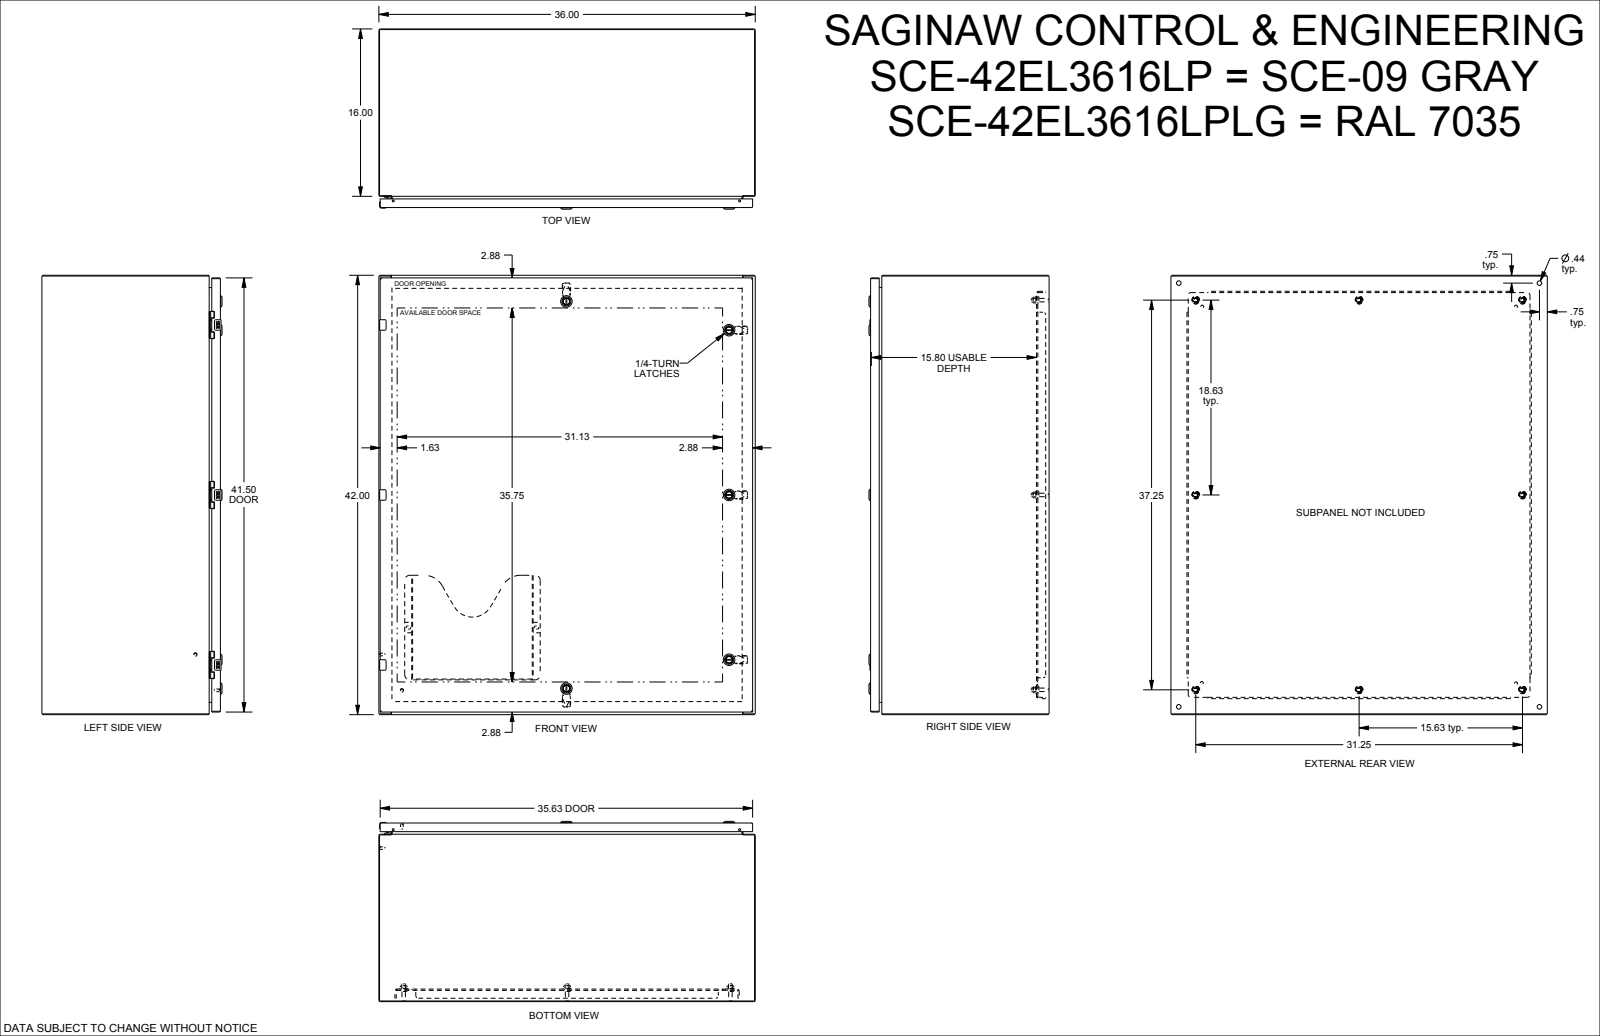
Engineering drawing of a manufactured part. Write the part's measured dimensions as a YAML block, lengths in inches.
part_name: "SCE-42EL3616LPLG"
step_written_by: "SolidWorks 2019 (CONFIG_CONTROL_DESIGN)"
units: inches
bodies: {solids: 0, faces: 4774, planar: 2327, cylindrical: 1328, other: 1119}
overall_size: [42, 36, 17.23]
round_holes:
  - {diameter: 0.367, count: 8}
  - {diameter: 0.5, count: 8}
  - {diameter: 0.172, count: 6}
  - {diameter: 0.205, count: 6}
  - {diameter: 0.244, count: 6}
  - {diameter: 0.266, count: 6}
  - {diameter: 0.375, count: 6}
  - {diameter: 0.197, count: 5}
  - {diameter: 0.315, count: 5}
  - {diameter: 0.394, count: 5}
  - {diameter: 0.634, count: 5}
  - {diameter: 0.281, count: 4}
round_bosses_or_shafts:
  - {diameter: 0.17, count: 9}
  - {diameter: 0.366, count: 8}
  - {diameter: 0.332, count: 8}
  - {diameter: 0.25, count: 6}
  - {diameter: 0.24, count: 6}
  - {diameter: 1.102, count: 5}
  - {diameter: 0.866, count: 5}
  - {diameter: 0.802, count: 5}
partial_cylinders:
  - {radius: 0.012, count: 136}
  - {radius: 0.01, count: 52}
  - {radius: 0.02, count: 52}
  - {radius: 0.015, count: 32}
  - {radius: 0.157, count: 20}
  - {radius: 0.04, count: 17}
  - {radius: 0.025, count: 16}
  - {radius: 0.1, count: 16}
face_to_face_distances: [0.075, 0.075, 16.998, 16.923, 17.073, 16.998, 1.2, 15.873, 35.925, 1]
hole_center_spacings: [16.25, 0.985, 32.5, 0.02, 0.493, 0.494, 4.493, 15.265]
